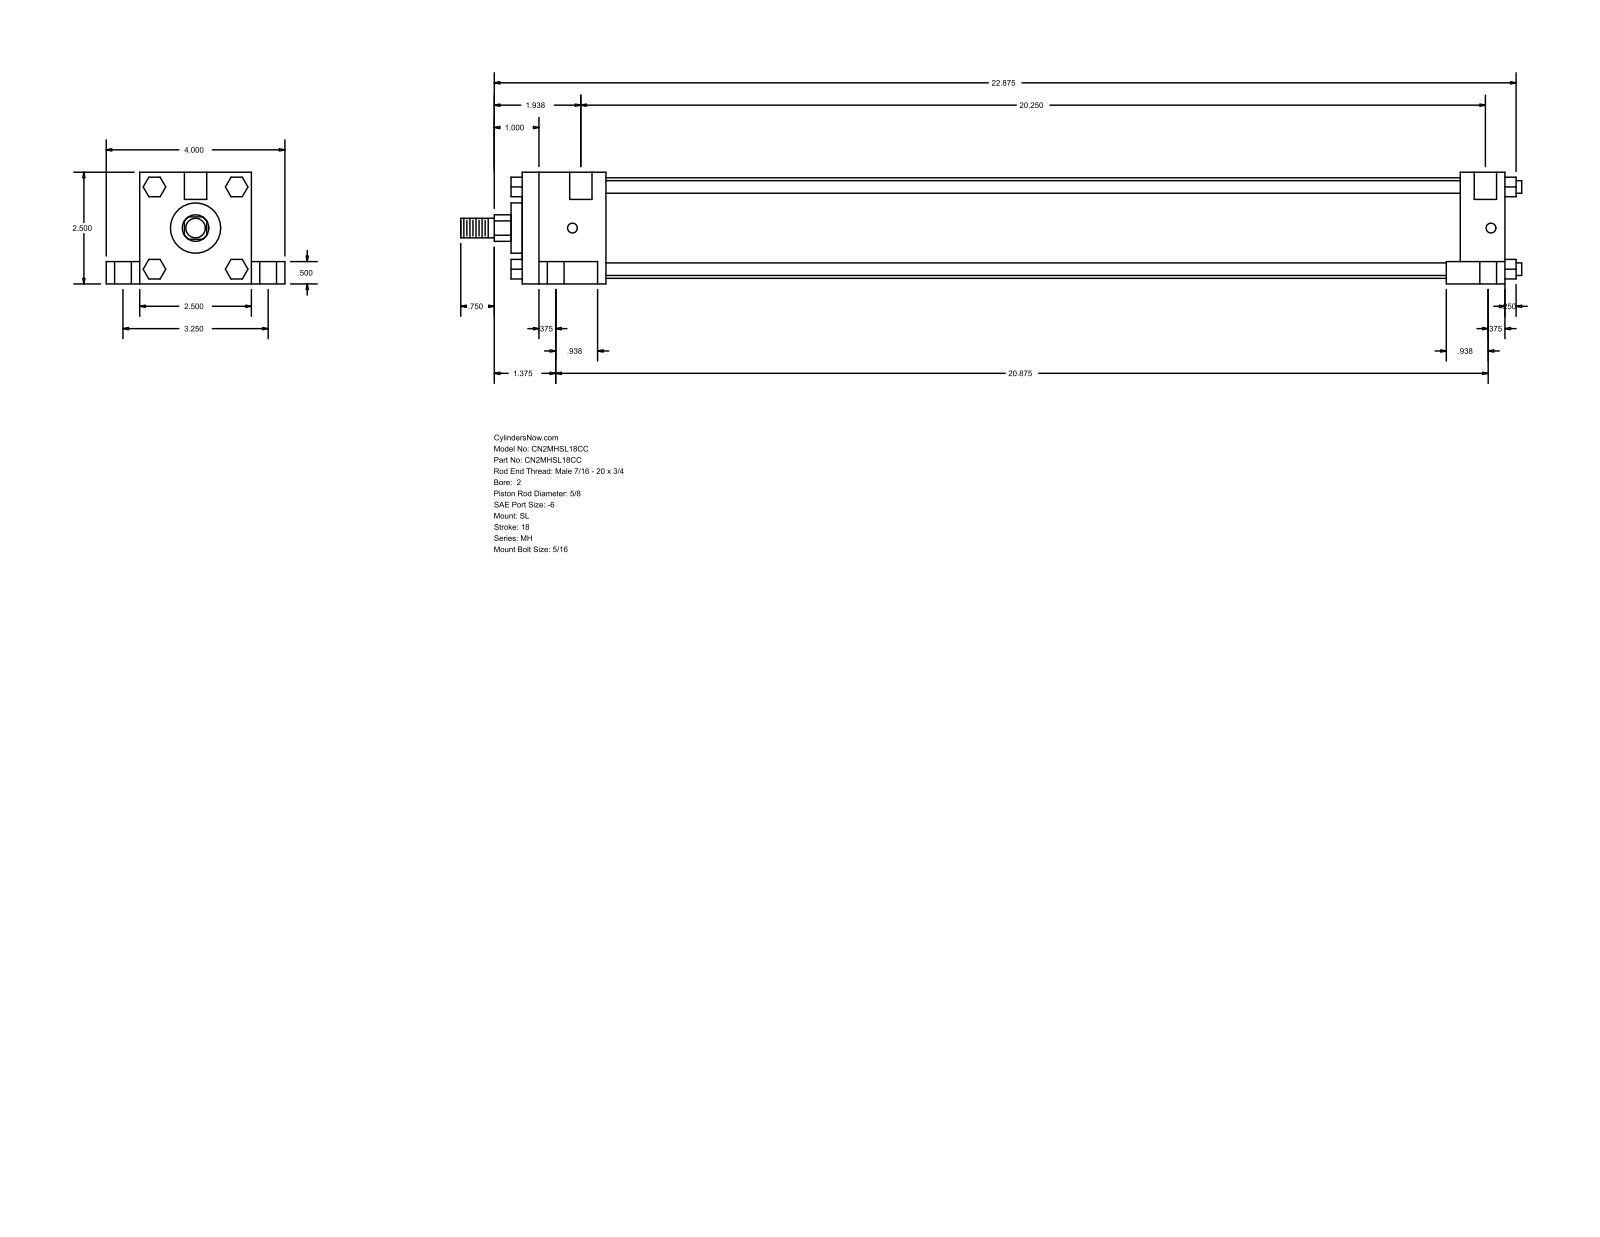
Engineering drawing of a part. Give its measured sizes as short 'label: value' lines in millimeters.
name: MH_SL__0200_0.625
written by: GSSL Pune (CONFIG_CONTROL_DESIGN)
unit: mm
bodies: 0 solids, 148 faces (112 planar, 36 cylindrical, 0 other)
size: 603.25 × 101.6 × 63.5
holes: 4× ⌀5.56, 4× ⌀9.53, 4× ⌀15.88, 2× ⌀12.7
bosses: 4× ⌀7.14, 1× ⌀57.15, 1× ⌀28.57, 1× ⌀15.88, 1× ⌀11.11
rounds: 1× R7.54
face distances: 63.5, 558.79, 12.7, 19.05, 82.55, 50.8, 25.4, 533.39, 47.62, 485.77
hole spacings: 41.3, 42.36, 43.67, 82.54, 517.59, 522.29, 522.33, 530.23
